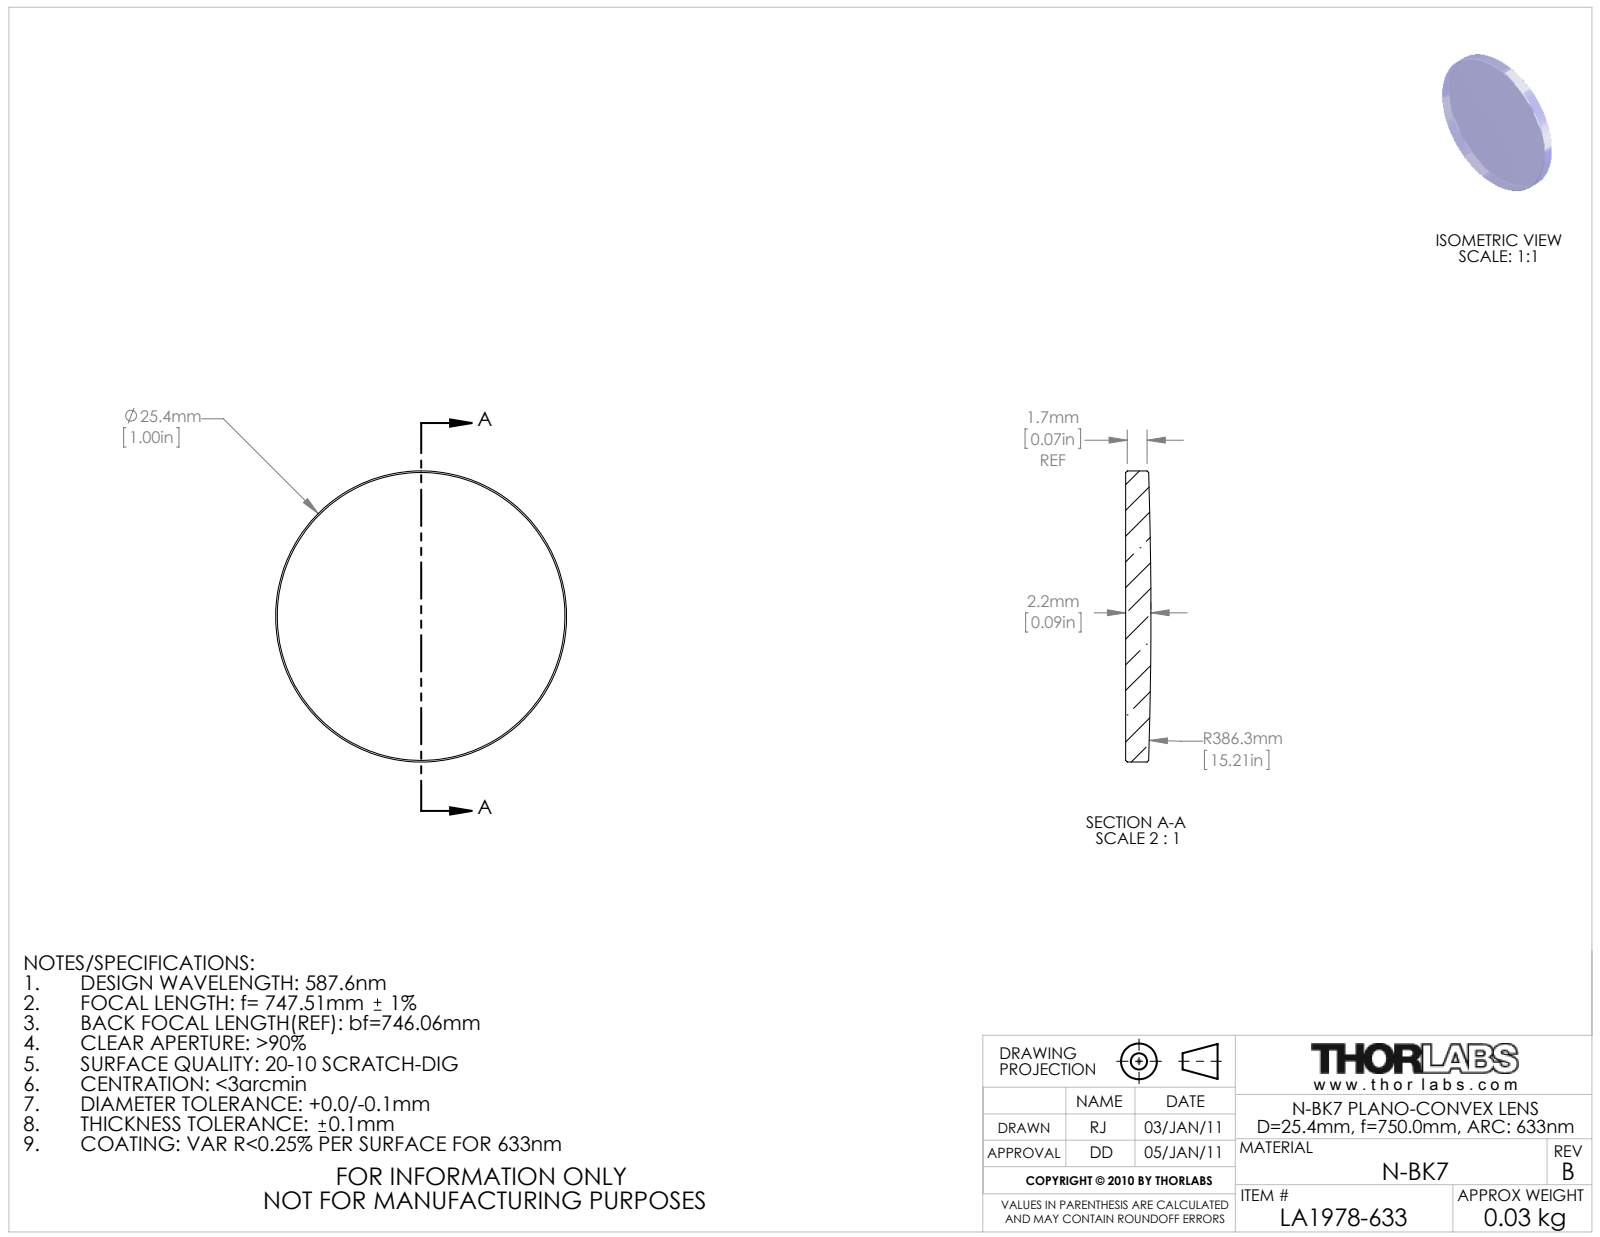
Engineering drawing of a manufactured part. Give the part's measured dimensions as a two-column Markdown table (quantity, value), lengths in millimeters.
| quantity | value |
| --- | --- |
| part name | 21804-E0W |
| STEP written by | SolidWorks 2011 (AUTOMOTIVE_DESIGN) |
| units | millimeters |
| bodies | 0 solids, 9 faces (1 planar, 2 cylindrical, 6 other) |
| overall size | 25.4 × 25.4 × 2.2 |
| round bosses / shafts (diameter × count) | 25.4 × 1 |
